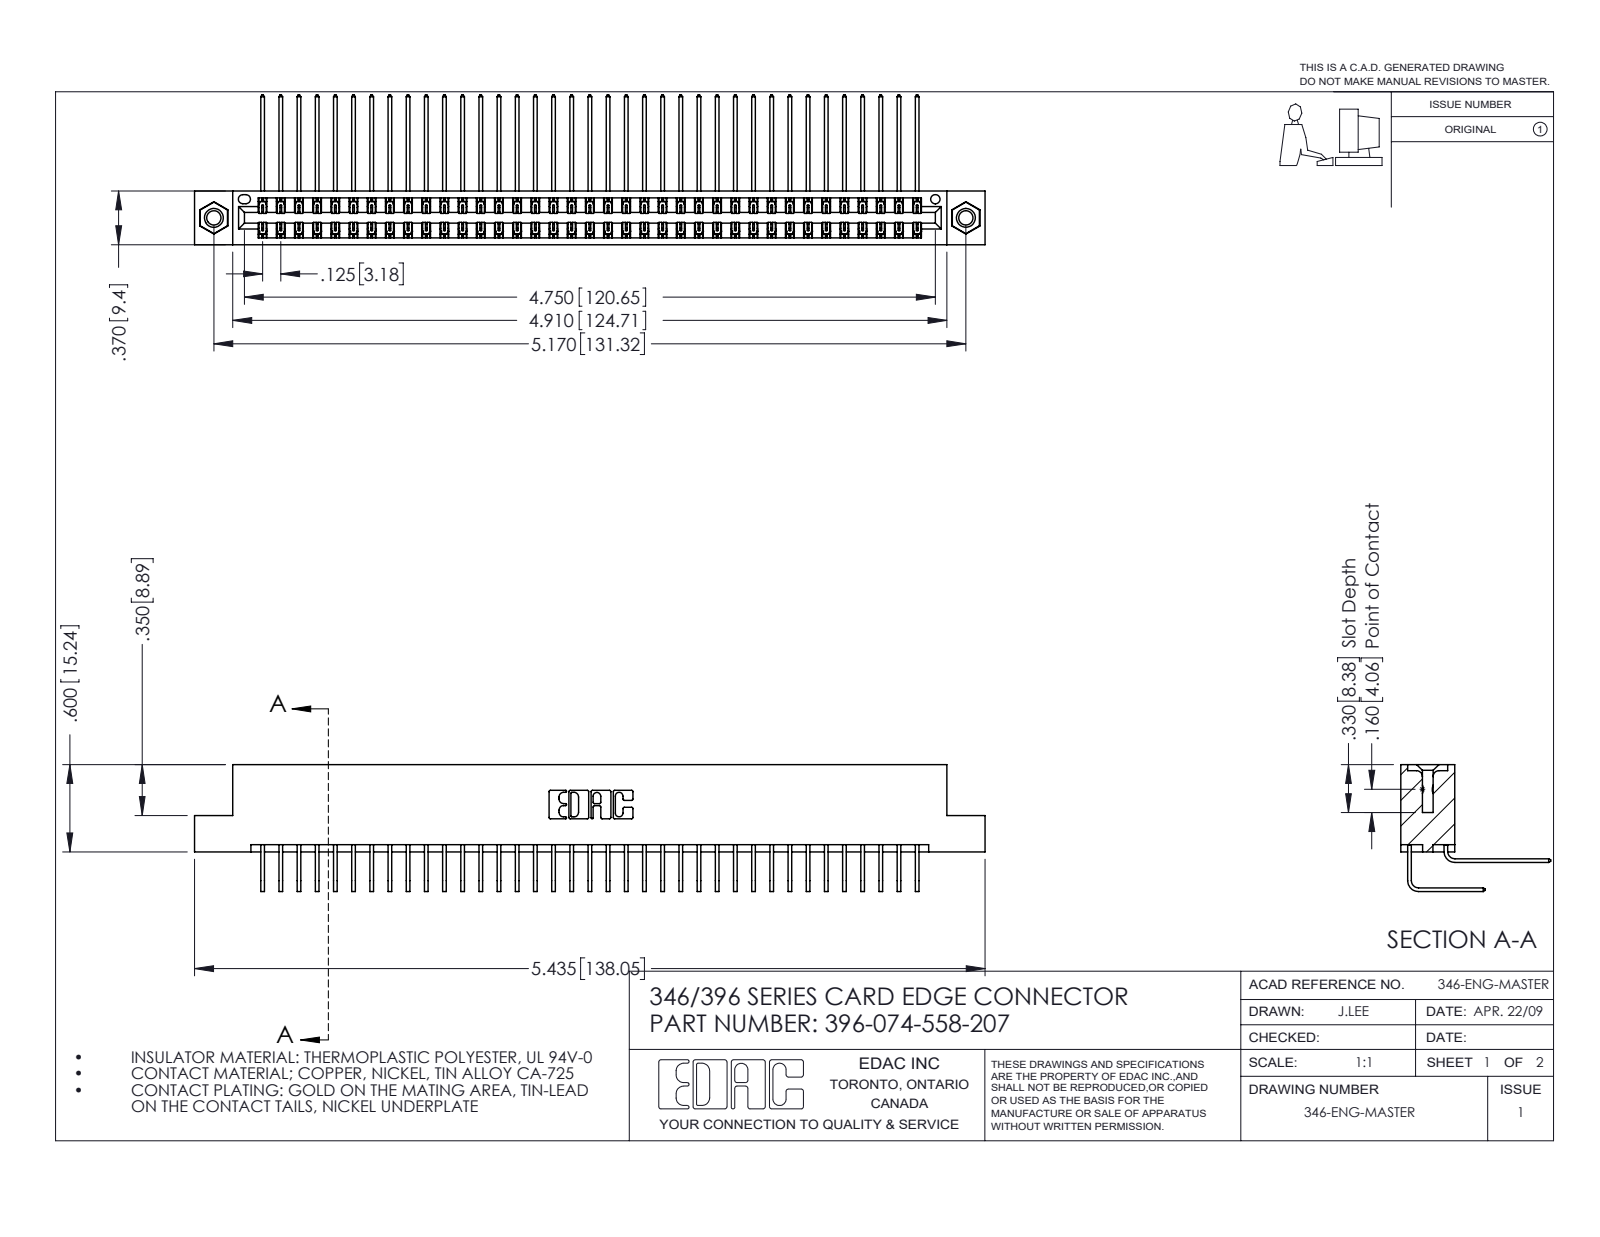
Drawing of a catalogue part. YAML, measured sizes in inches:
part_name: "345-292-001_558 559 Tail - 1; 396-074-558-207; 346 Part_Flush Mounting Lugs - 0.156 Dia-TI; 345-292-001_558 Tail - 2 (+1 more)"
step_written_by: "SolidWorks 2016 (CONFIG_CONTROL_DESIGN)"
units: inches
bodies: {solids: 77, faces: 4178, planar: 2846, cylindrical: 1316, other: 16}
overall_size: [5.435, 1.03, 0.873]
volume: 0.844
surface_area: 32.58
round_holes:
  - {diameter: 0.098, count: 2}
  - {diameter: 0.125, count: 2}
  - {diameter: 0.156, count: 2}
  - {diameter: 0.064, count: 1}
round_bosses_or_shafts:
  - {diameter: 0.155, count: 2}
partial_cylinders:
  - {radius: 0.006, count: 111}
  - {radius: 0.01, count: 22}
  - {radius: 0.007, count: 6}
  - {radius: 0.031, count: 6}
  - {radius: 0.026, count: 3}
  - {radius: 0.014, count: 2}
  - {radius: 0.022, count: 2}
  - {radius: 0.024, count: 2}
face_to_face_distances: [0.048, 0.322, 0.025, 0.37, 0.25, 0.072, 0.298, 0.275, 0.148, 0.222]
hole_center_spacings: [0.246, 4.961, 5.17]
